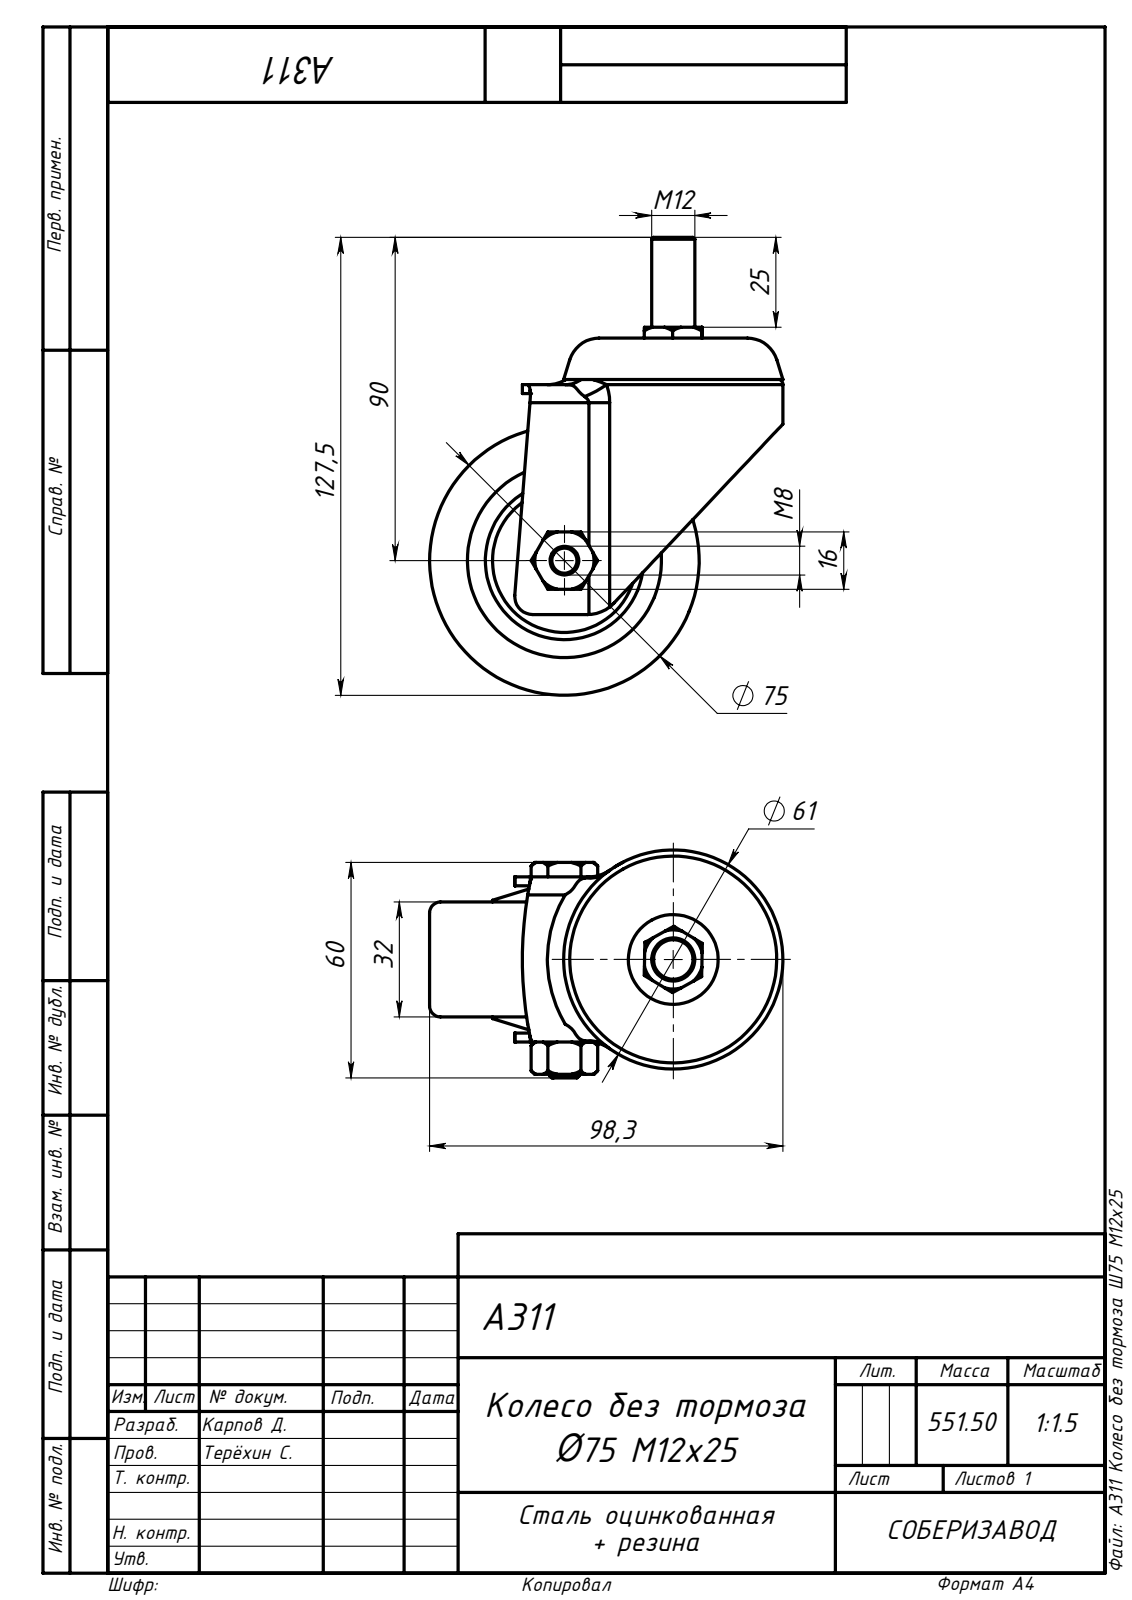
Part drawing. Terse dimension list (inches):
name: A311 Болт_00; Болт_00; Защита_00; Крышка_00 (+5 more)
written by: SolidWorks 2021 (AUTOMOTIVE_DESIGN)
unit: in
bodies: 9 solids, 207 faces (61 planar, 51 cylindrical, 95 other)
size: 5.02 × 3.87 × 2.5
volume: 9.921 in³; area: 98.14 in²
holes: 2× ⌀0.394, 1× ⌀0.236, 1× ⌀1.417, 1× ⌀1.732
bosses: 1× ⌀2.953, 1× ⌀1.575, 1× ⌀0.472, 1× ⌀0.315
rounds: 3× R0.197, 3× R0.394, 1× R1.102, 1× R1.201, 1× R4.206
face distances: 0.098, 0.177, 1.437, 0.276, 1.535, 1.713, 0.689, 0.787, 1.024, 0.925
